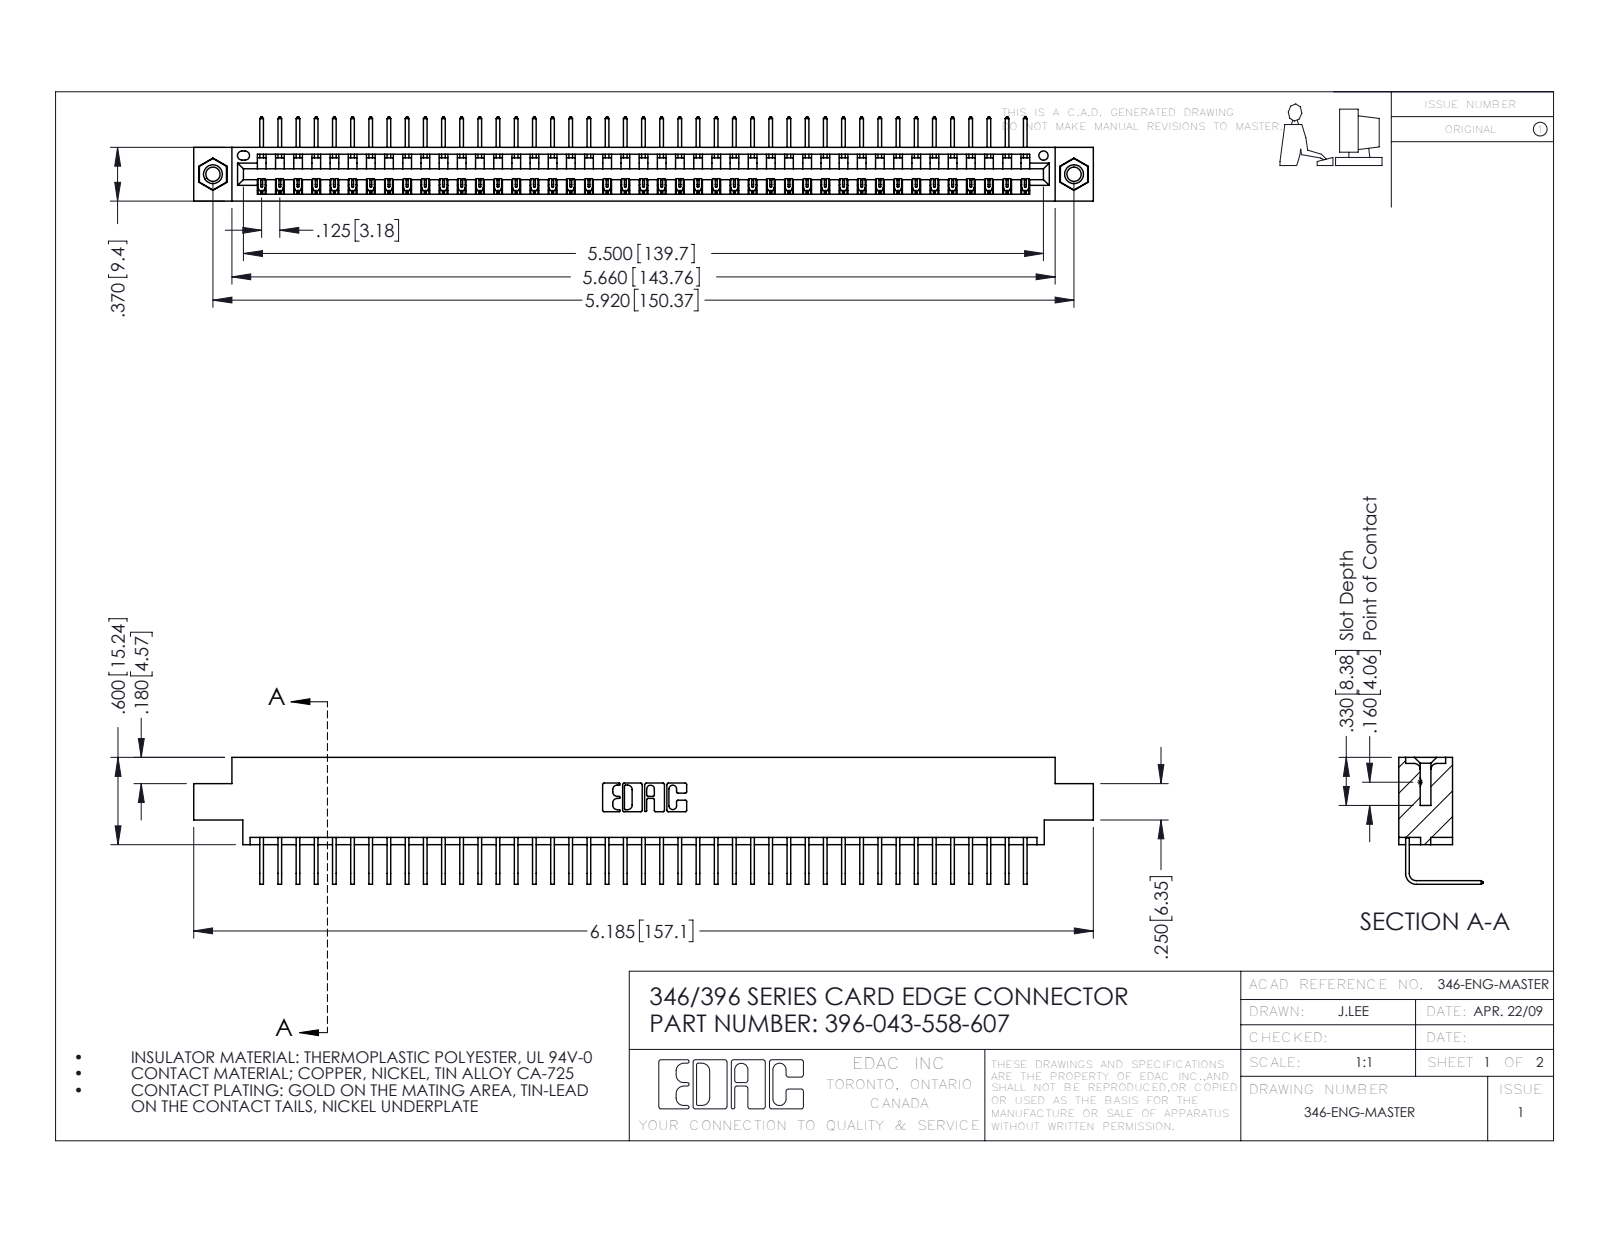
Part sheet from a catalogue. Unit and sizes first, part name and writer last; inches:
Units: inches
Overall size (bounding box): 6.185 × 0.873 × 0.58
Round holes (diameter × count): ⌀0.098 ×2, ⌀0.125 ×2, ⌀0.156 ×2, ⌀0.064 ×1
Round bosses / shafts (diameter × count): ⌀0.155 ×2
Partial cylindrical surfaces — rounded edges, fillets, slot ends (radius × count): R0.006 ×86, R0.01 ×22, R0.007 ×6, R0.031 ×6, R0.026 ×3, R0.031 ×2, R0.04 ×2, R0.014 ×1
Main face-to-face distances: 0.322, 0.048, 0.37, 0.25, 0.298, 0.025, 0.072, 0.222, 0.148, 0.1
Hole centre spacings: 0.246, 5.711, 5.92
Volume: 0.917 in³ · Surface area: 30.74 in²
Bodies: 46 solids, 2766 faces (1918 planar, 832 cylindrical, 16 other)
Part name (STEP PRODUCT): 346 Part_0.170 Offset - 0.156 Dia-TI; 345-250-001_345-250-005-103; 396-043-558-607; 345-292-001_558 Tail - 2
STEP written by: SolidWorks 2016 (CONFIG_CONTROL_DESIGN)
